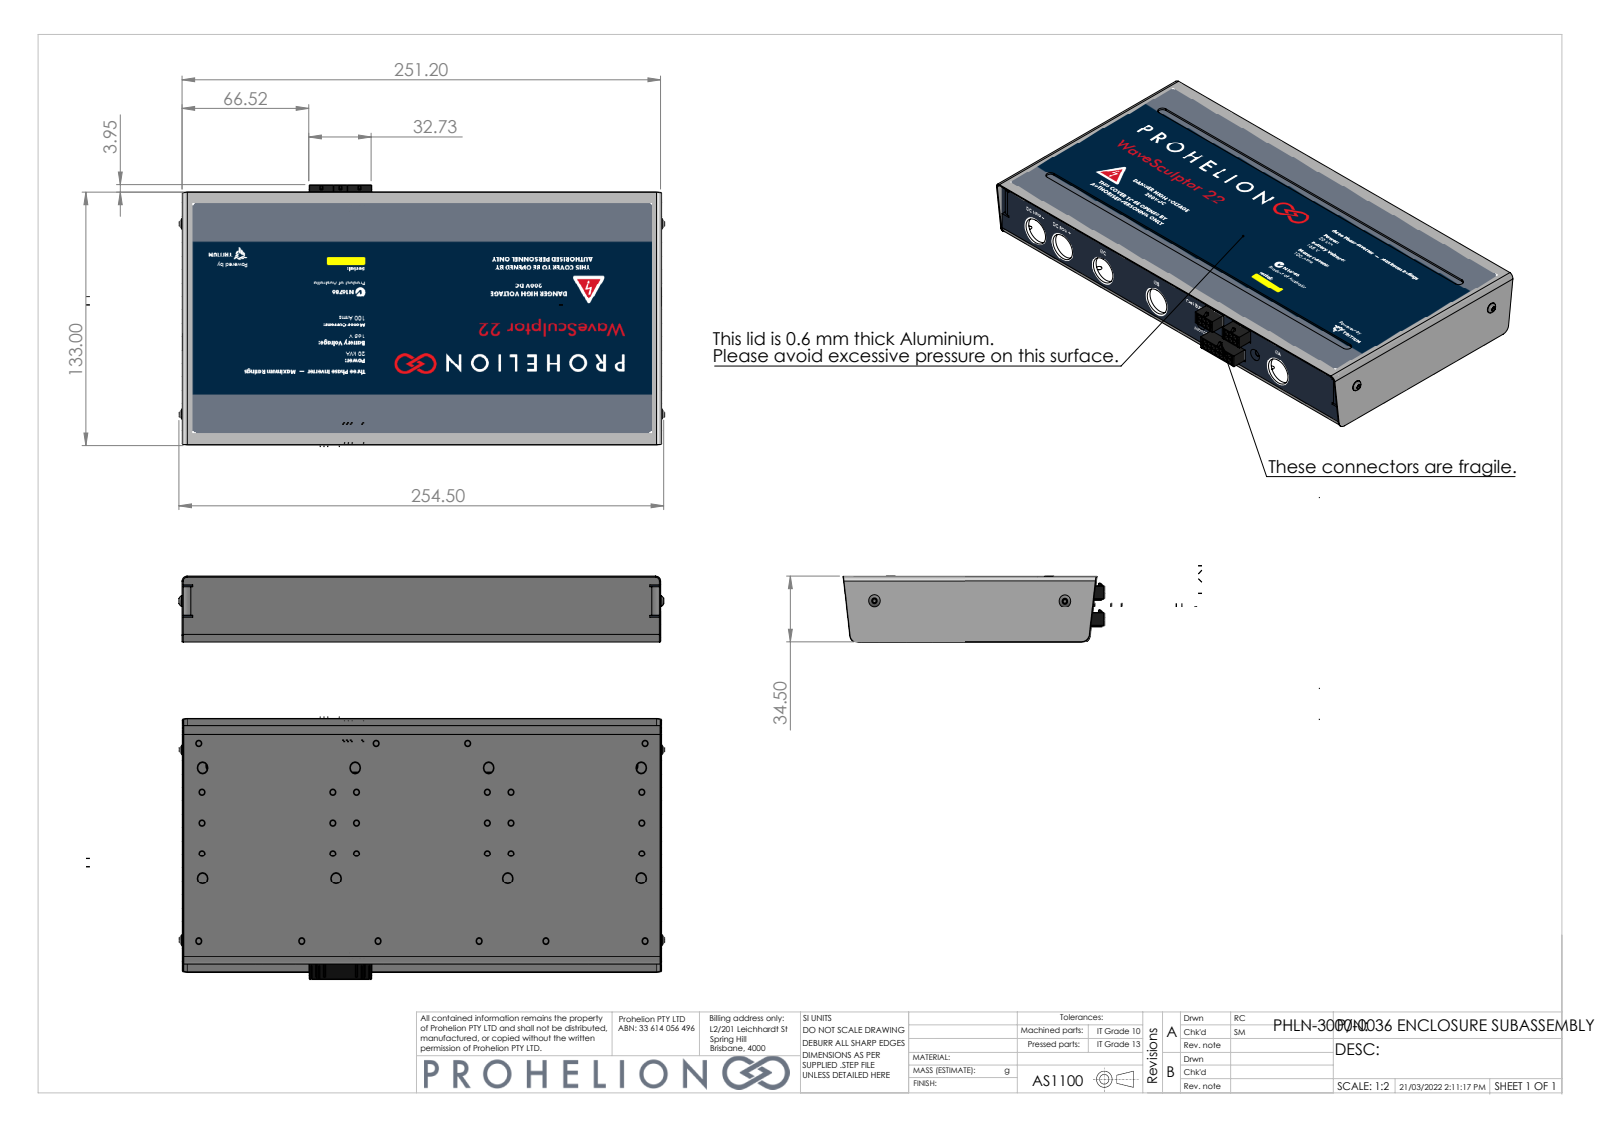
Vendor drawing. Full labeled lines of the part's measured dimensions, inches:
Part name (STEP PRODUCT): 6861xx188822_Pin1.step; PHLN-3000-0027.step; 6861xx188822_Pin1-3.step; 66201421122.step (+8 more)
STEP written by: SolidWorks 2021 (AUTOMOTIVE_DESIGN)
Units: inches
Bodies: 62 solids, 3241 faces (2457 planar, 724 cylindrical, 60 other)
Overall size (bounding box): 10.02 × 5.392 × 1.362
Volume: 7.459 in³ · Surface area: 297.4 in²
Round holes (diameter × count): ⌀0.118 ×30, ⌀0.213 ×8, ⌀0.571 ×5, ⌀0.097 ×2, ⌀0.138 ×2, ⌀0.167 ×2
Round bosses / shafts (diameter × count): ⌀0.026 ×6, ⌀0.236 ×2, ⌀0.224 ×2, ⌀0.165 ×2, ⌀0.118 ×2
Partial cylindrical surfaces — rounded edges, fillets, slot ends (radius × count): R0.004 ×80, R0.019 ×80, R0.079 ×8, R0.079 ×8, R0.157 ×8, R0.025 ×6, R0.029 ×6, R0.029 ×6
Main face-to-face distances: 0.079, 0.024, 1.339, 1.362, 1.26, 1.283, 4.843, 9.866, 4.764, 4.921
Hole centre spacings: 3.251, 0.63, 2.773, 3.189, 2.701, 0.797, 3.429, 5.923
